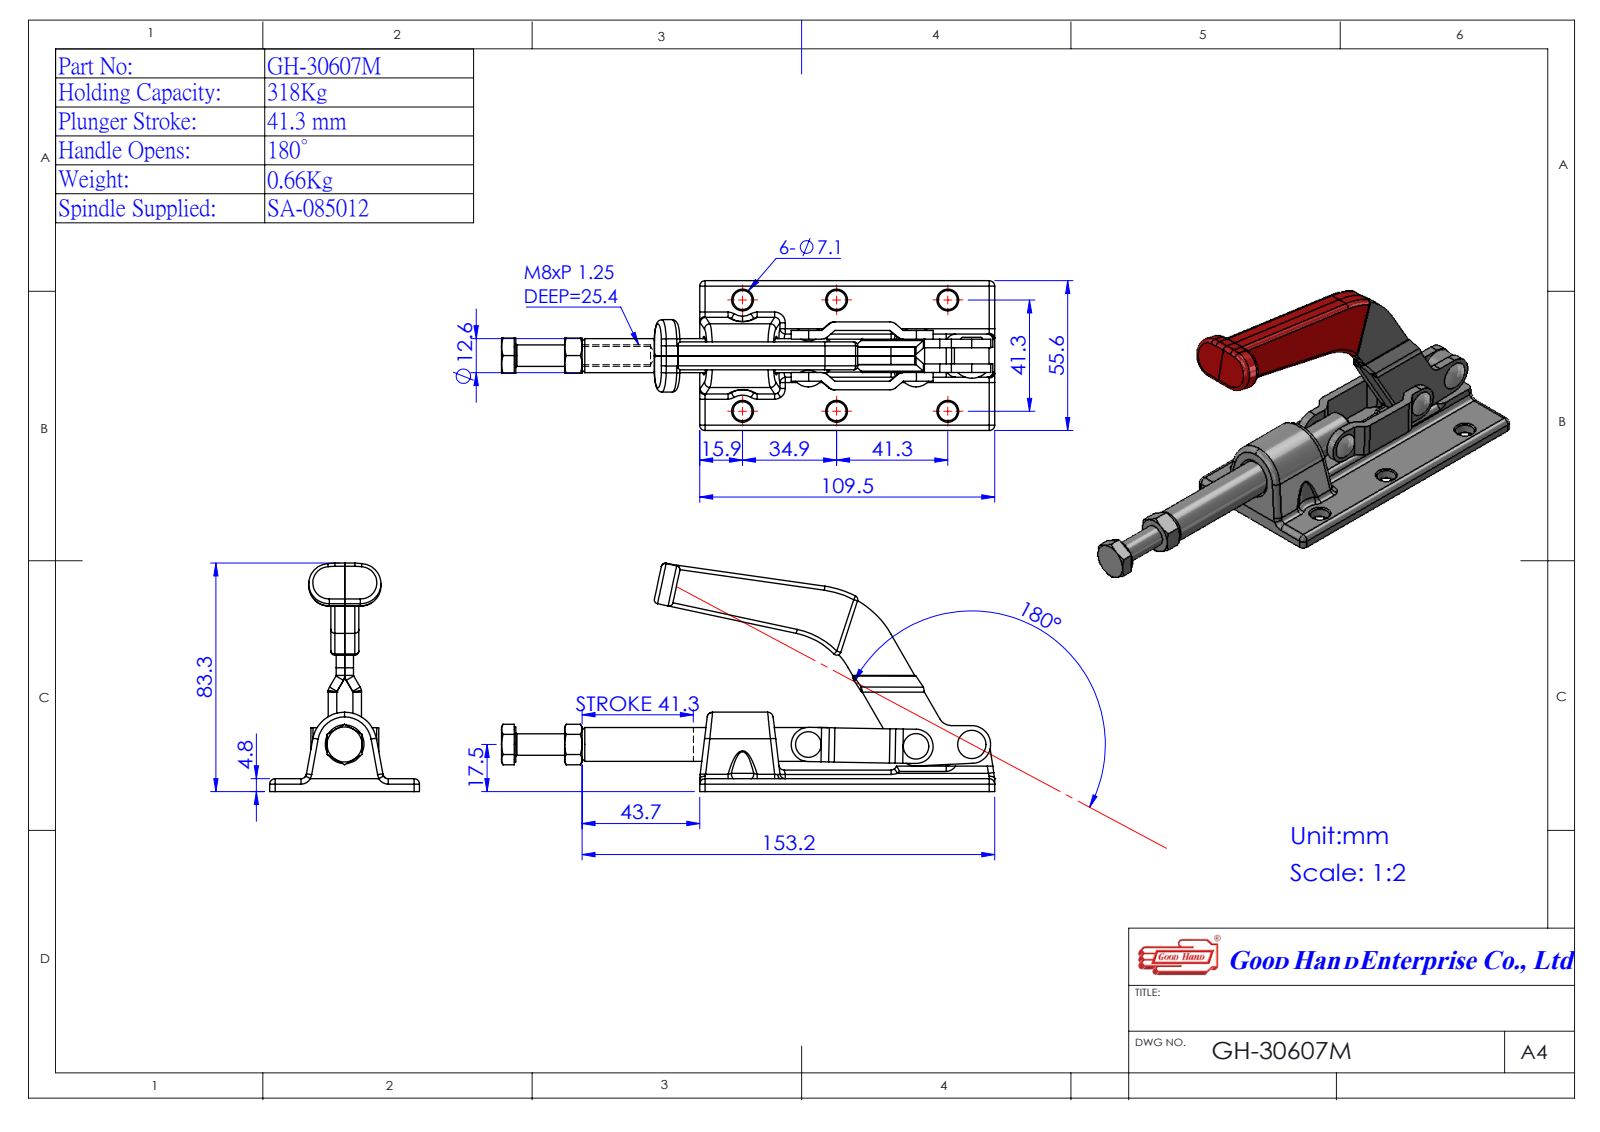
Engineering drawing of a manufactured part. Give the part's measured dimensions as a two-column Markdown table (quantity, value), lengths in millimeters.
| quantity | value |
| --- | --- |
| part name | Group1^493792(GH-30607M); Group2^493792(GH-30607M); 493792(GH-30607M); 3302713-1^493792(GH-30607M) (+1 more) |
| STEP written by | SolidWorks 2016 (AUTOMOTIVE_DESIGN) |
| units | millimeters |
| bodies | 4 solids, 249 faces (145 planar, 78 cylindrical, 26 other) |
| overall size | 188.49 × 85.1 × 55.6 |
| volume | 89 210 mm³ |
| surface area | 37 940 mm² |
| round holes (diameter × count) | 7.1 × 6, 5 × 3, 12.6 × 1 |
| round bosses / shafts (diameter × count) | 8 × 1 |
| partial cylindrical surfaces (radius × count) | 3.2 × 8, 0.5 × 4, 3.7 × 4, 6.35 × 2, 7.64 × 2, 8 × 2, 2 × 1, 5 × 1 |
| main face-to-face distances | 4.8, 3.2, 1, 11.4, 9.2, 2.2, 8.2, 6.4, 9.4, 6.2 |
| hole center spacings | 41.3, 34.9, 54.07, 58.41, 76.2, 86.67, 20.7, 40 |
